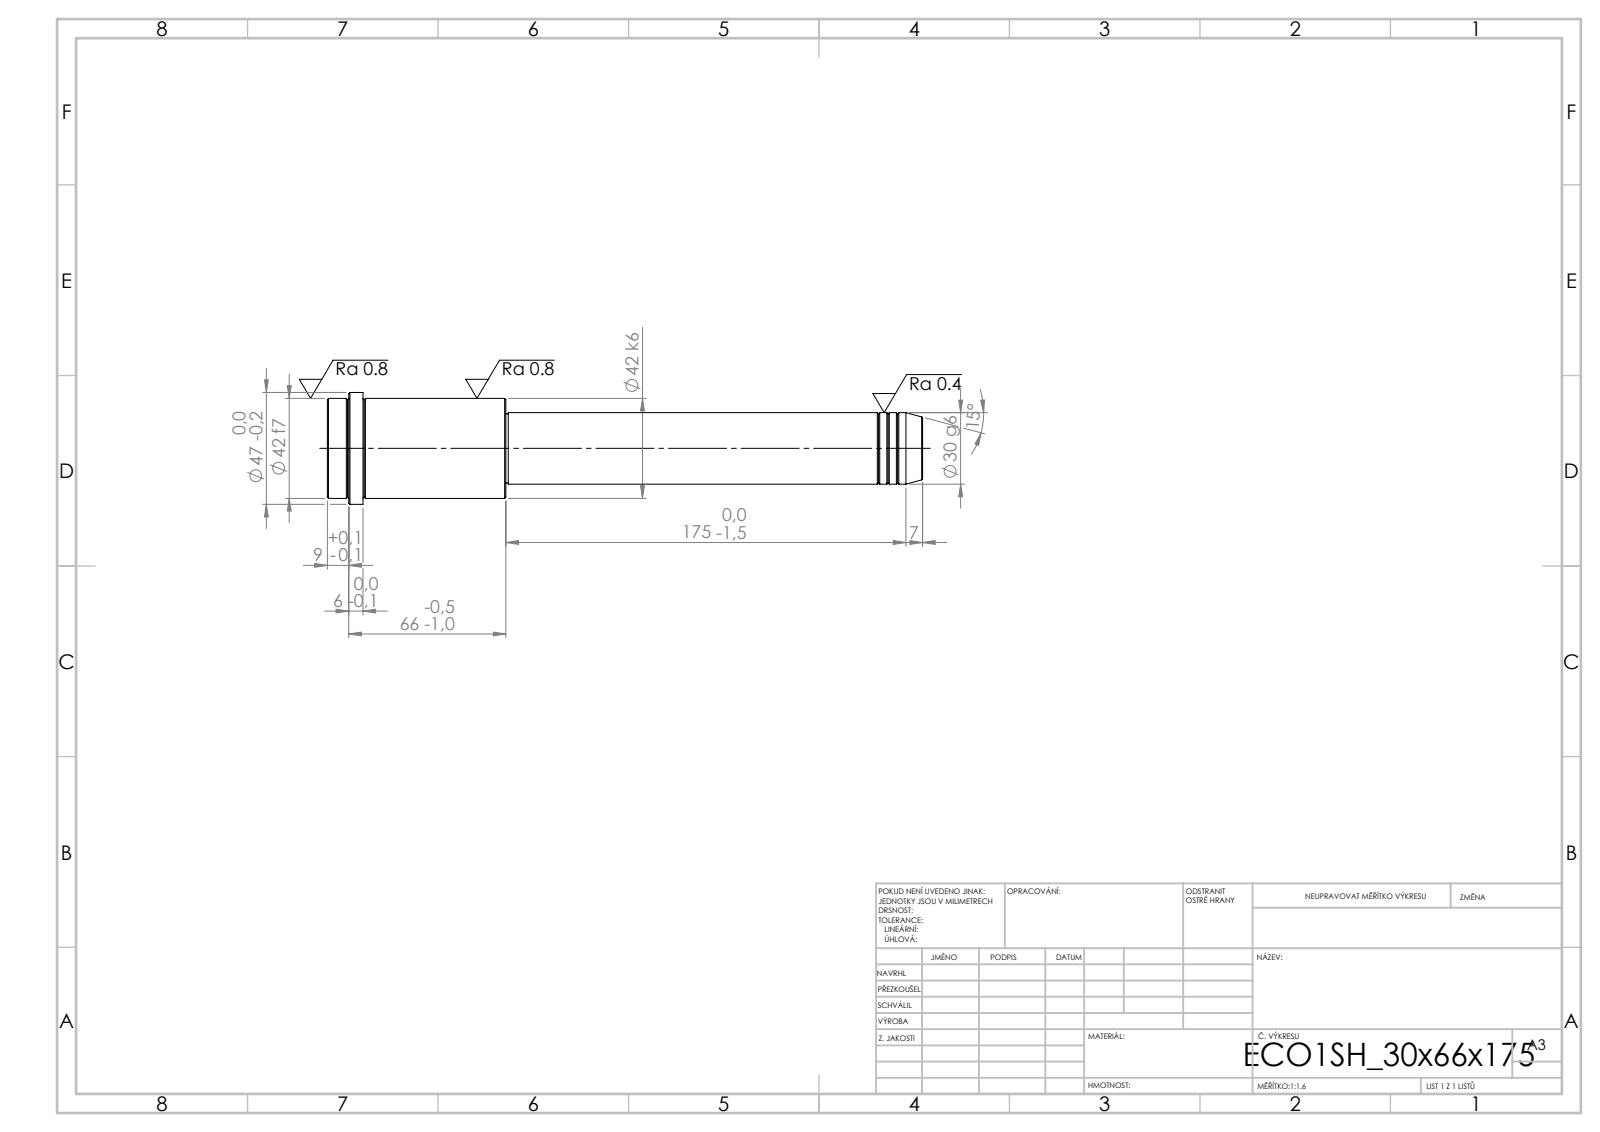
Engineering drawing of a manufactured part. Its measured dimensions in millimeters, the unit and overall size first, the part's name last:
Units: millimetres
Overall size (bounding box): 250 × 47 × 47
Round bosses / shafts (diameter × count): ⌀47 ×1, ⌀42 ×1, ⌀30 ×1, ⌀29 ×1
Main face-to-face distances: 75, 175, 250, 235, 60, 15, 241, 66, 6, 9
Volume: 228 801 mm³ · Surface area: 30 023 mm²
Bodies: 1 solid, 52 faces (6 planar, 16 cylindrical, 30 other)
STEP written by: SolidWorks 2019 (CONFIG_CONTROL_DESIGN)
